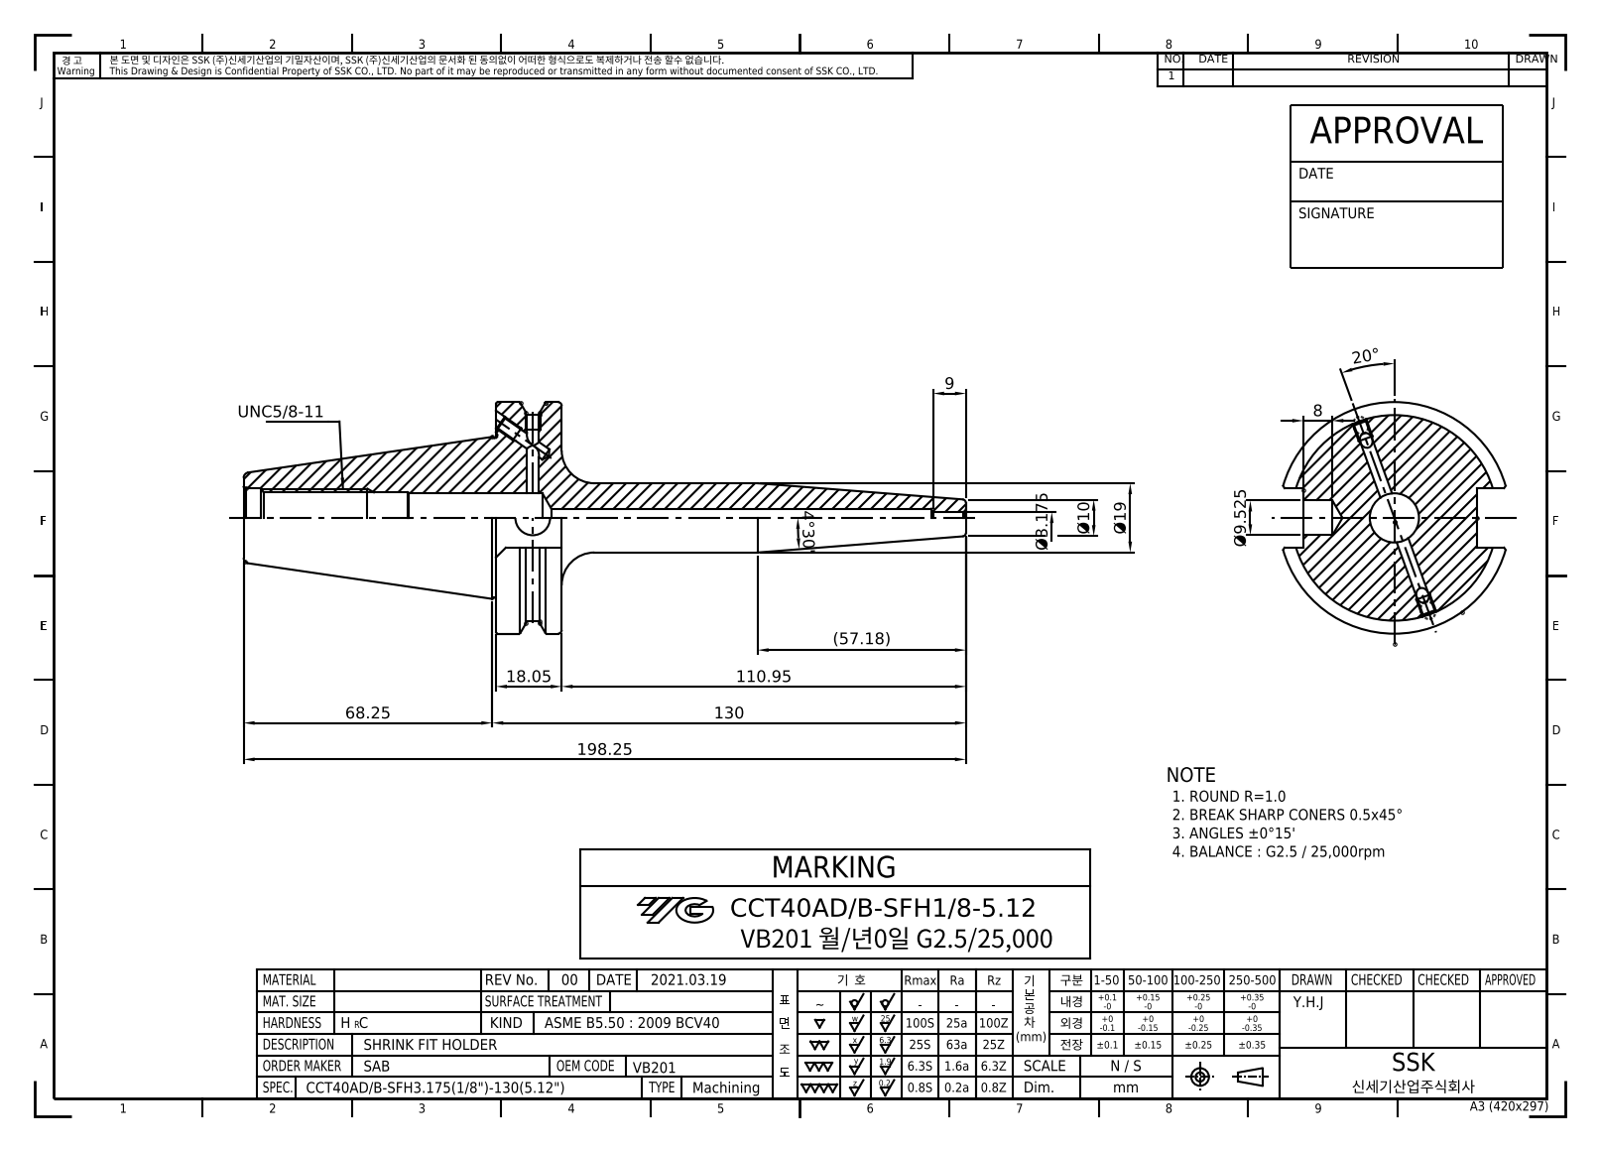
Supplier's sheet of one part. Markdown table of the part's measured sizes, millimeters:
| quantity | value |
| --- | --- |
| part name | LO CCT40ADB-SFH3.175-5.12 |
| STEP written by | Autodesk Inventor 2022 (AUTOMOTIVE_DESIGN) |
| units | millimeters |
| bodies | 1 solid, 88 faces (36 planar, 28 cylindrical, 24 other) |
| overall size | 198.25 × 63.5 × 61.09 |
| volume | 127 841 mm³ |
| surface area | 28 367 mm² |
| round holes (diameter × count) | 3.24 × 4, 4 × 2, 4.2 × 2, 3.17 × 1, 5 × 1, 9.53 × 1, 13 × 1, 13.39 × 1, 16.3 × 1 |
| round bosses / shafts (diameter × count) | 63.5 × 1, 43.8 × 1, 19 × 1 |
| partial cylindrical surfaces (radius × count) | 28.15 × 1 |
| main face-to-face distances | 18.05, 47.6, 16.38, 69.25, 87.3, 81.34, 12.09, 5.96, 77.51, 8.26 |
